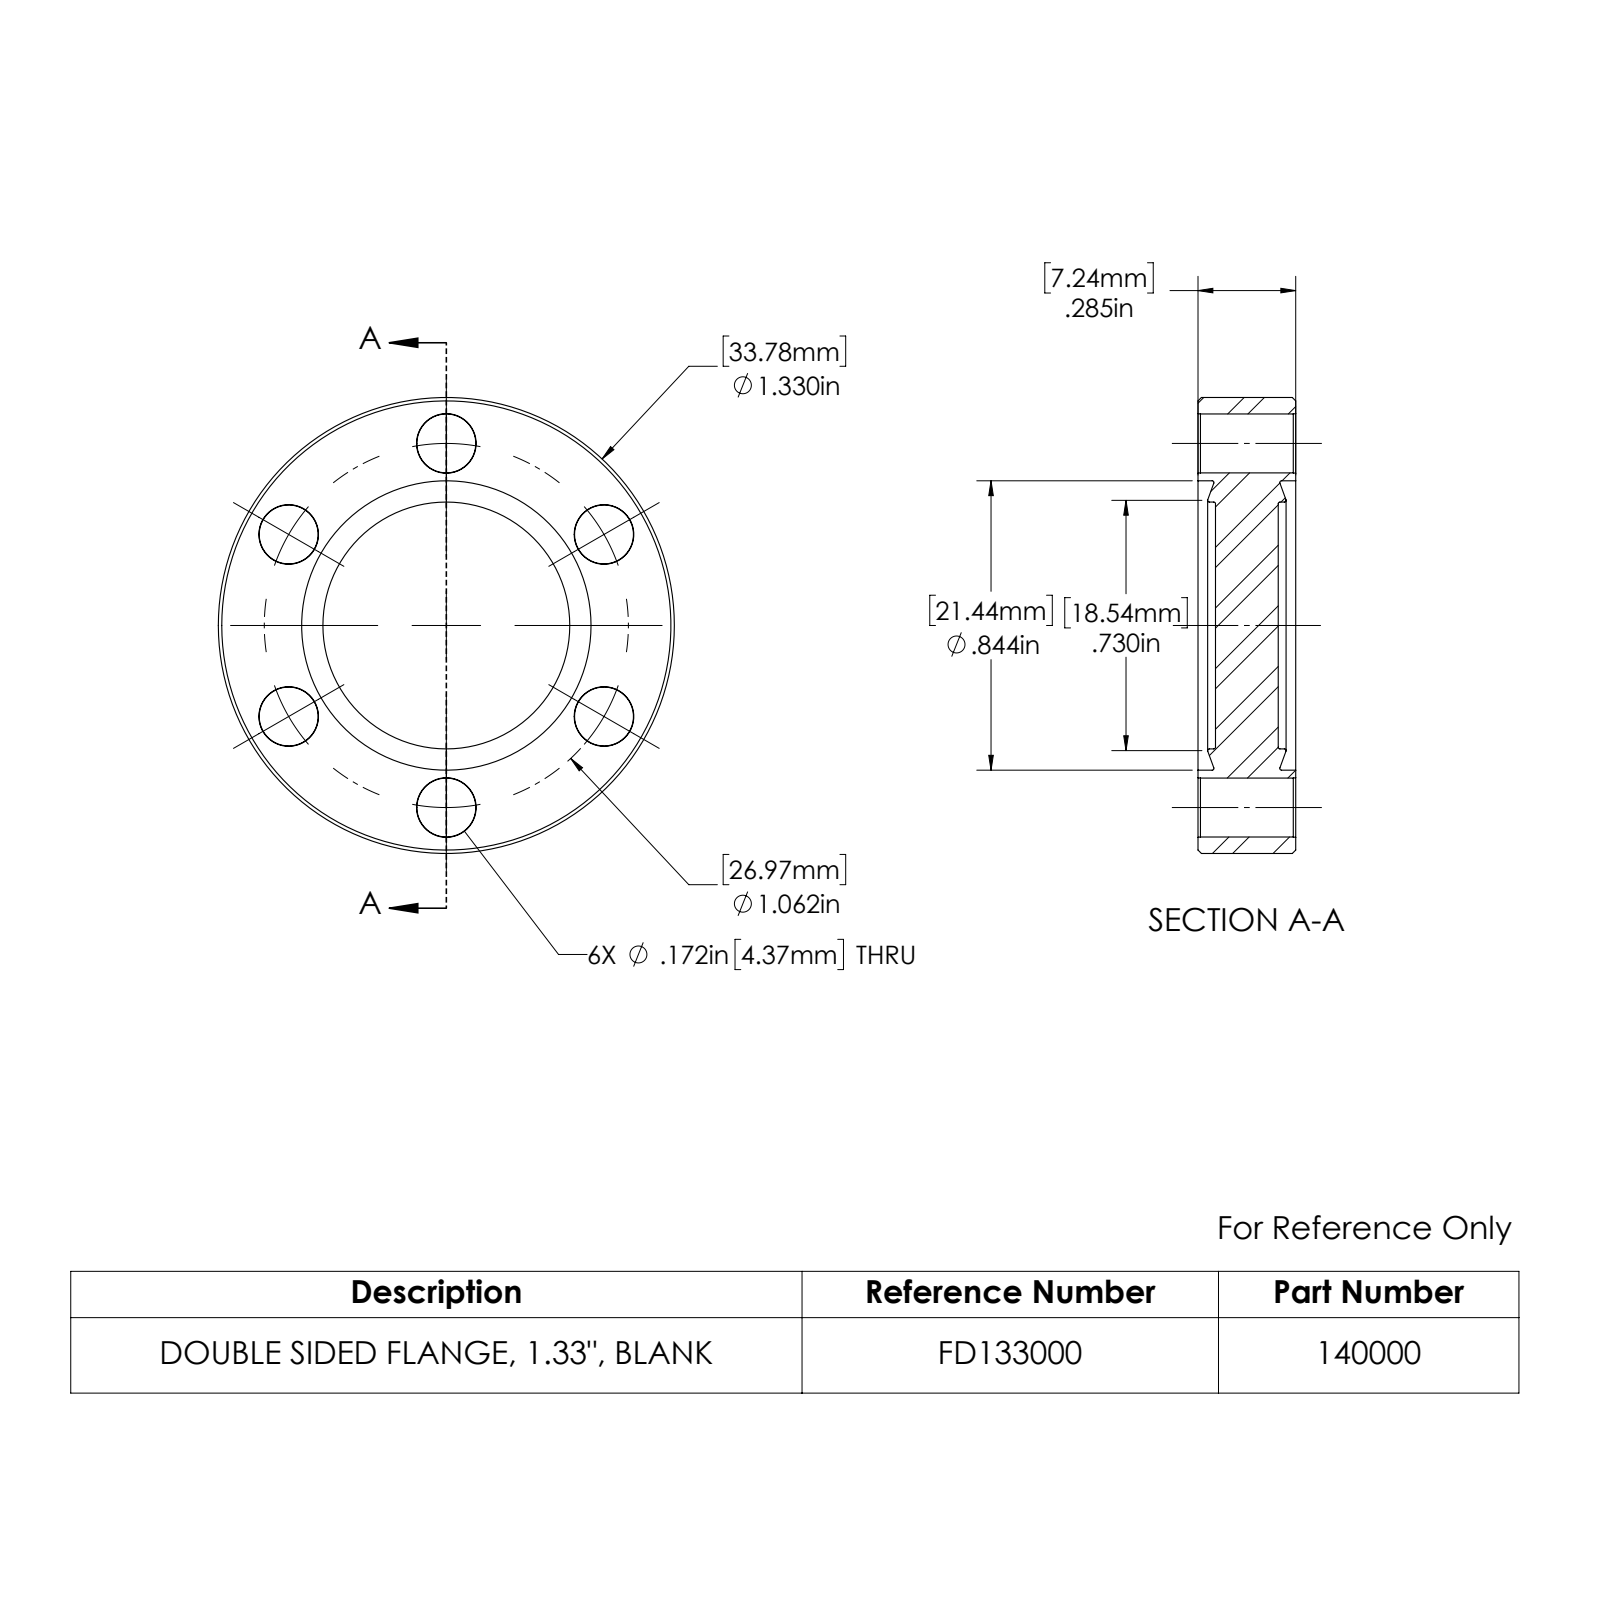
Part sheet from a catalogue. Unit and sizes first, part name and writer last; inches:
Units: inches
Overall size (bounding box): 1.33 × 1.33 × 0.285
Round holes (diameter × count): ⌀0.172 ×6, ⌀0.72 ×1, ⌀0.844 ×1
Round bosses / shafts (diameter × count): ⌀1.33 ×1
Main face-to-face distances: 0.051, 0.234, 0.285, 0.183
Hole centre spacings: 0.531, 0.92, 0.531, 1.062, 1.062
Volume: 0.303 in³ · Surface area: 4.894 in²
Bodies: 1 solid, 70 faces (4 planar, 22 cylindrical, 44 other)
Part name (STEP PRODUCT): 140000_A
STEP written by: SolidWorks 2022 (CONFIG_CONTROL_DESIGN)
